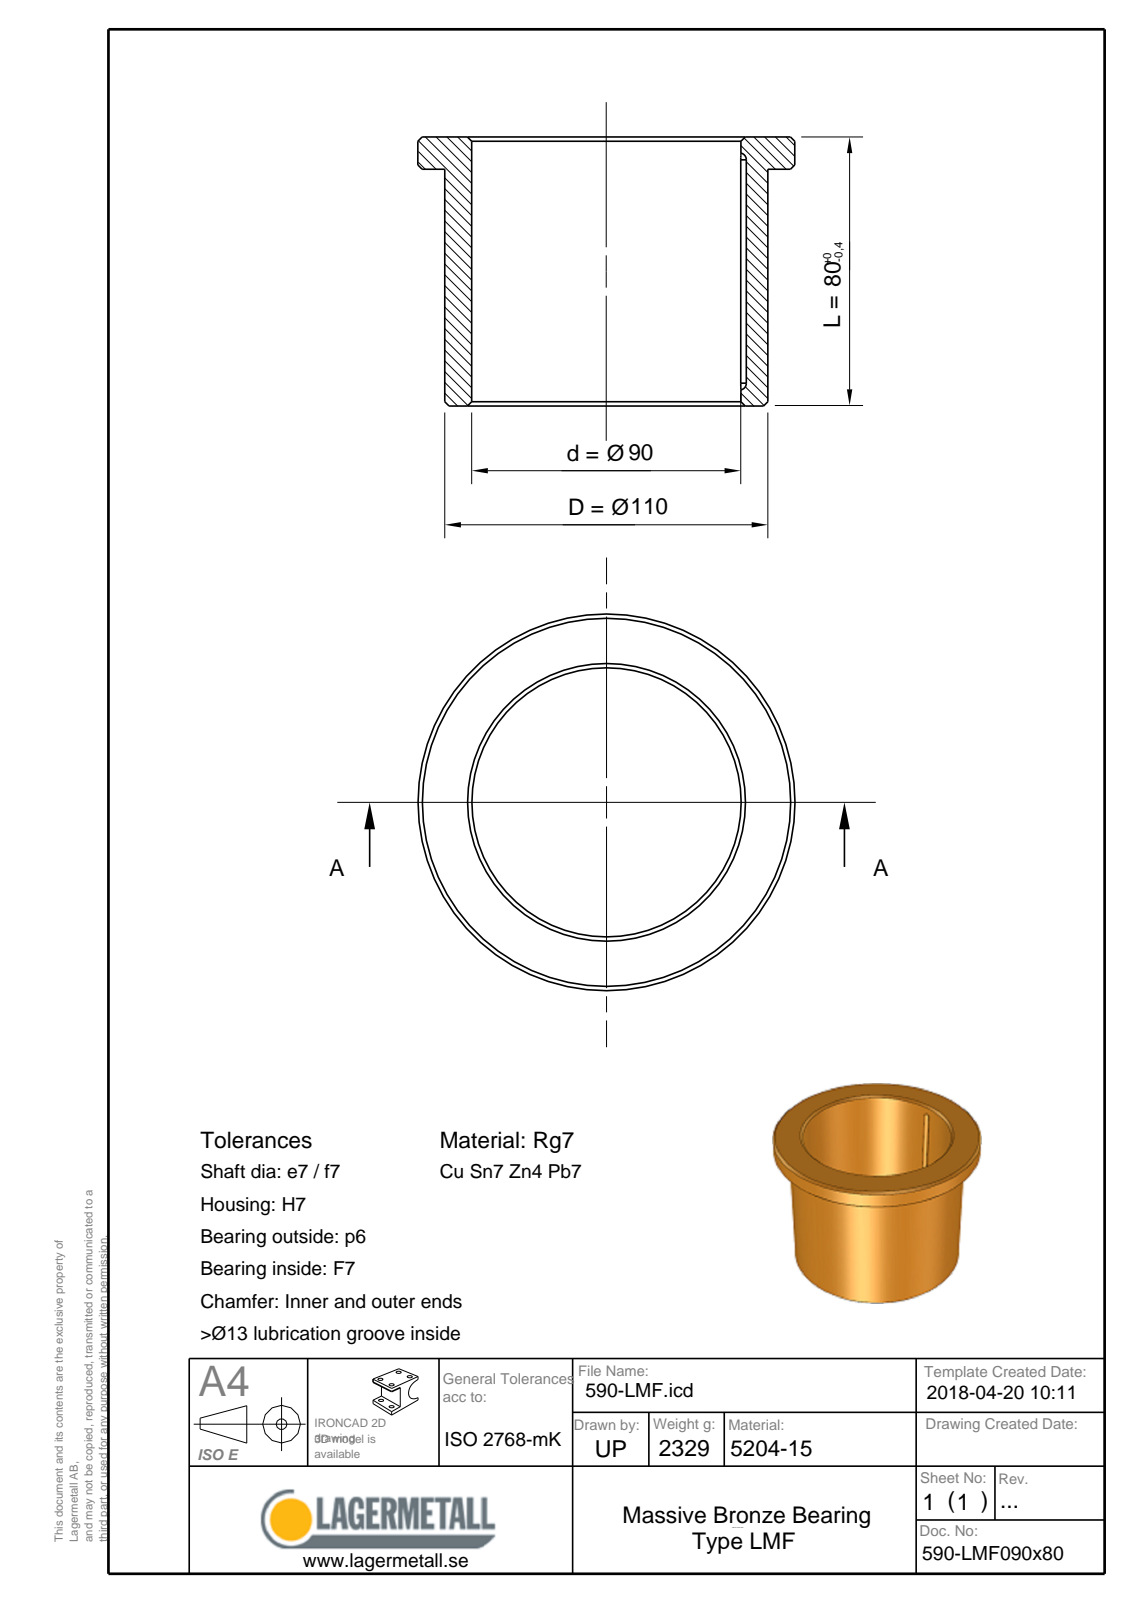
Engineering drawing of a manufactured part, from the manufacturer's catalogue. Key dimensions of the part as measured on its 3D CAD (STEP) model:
Part name (STEP PRODUCT): 590-LMF090x80
STEP written by: Spatial InterOp 3D (CONFIG_CONTROL_DESIGN)
Units: millimetres
Bodies: 1 solid, 16 faces (4 planar, 5 cylindrical, 7 other)
Overall size (bounding box): 120 × 120 × 80
Volume: 264 663 mm³ · Surface area: 59 552 mm²
Round holes (diameter × count): ⌀90 ×1
Round bosses / shafts (diameter × count): ⌀120 ×1, ⌀110 ×1
Partial cylindrical surfaces — rounded edges, fillets, slot ends (radius × count): R1.75 ×2
Main face-to-face distances: 80, 72, 8
